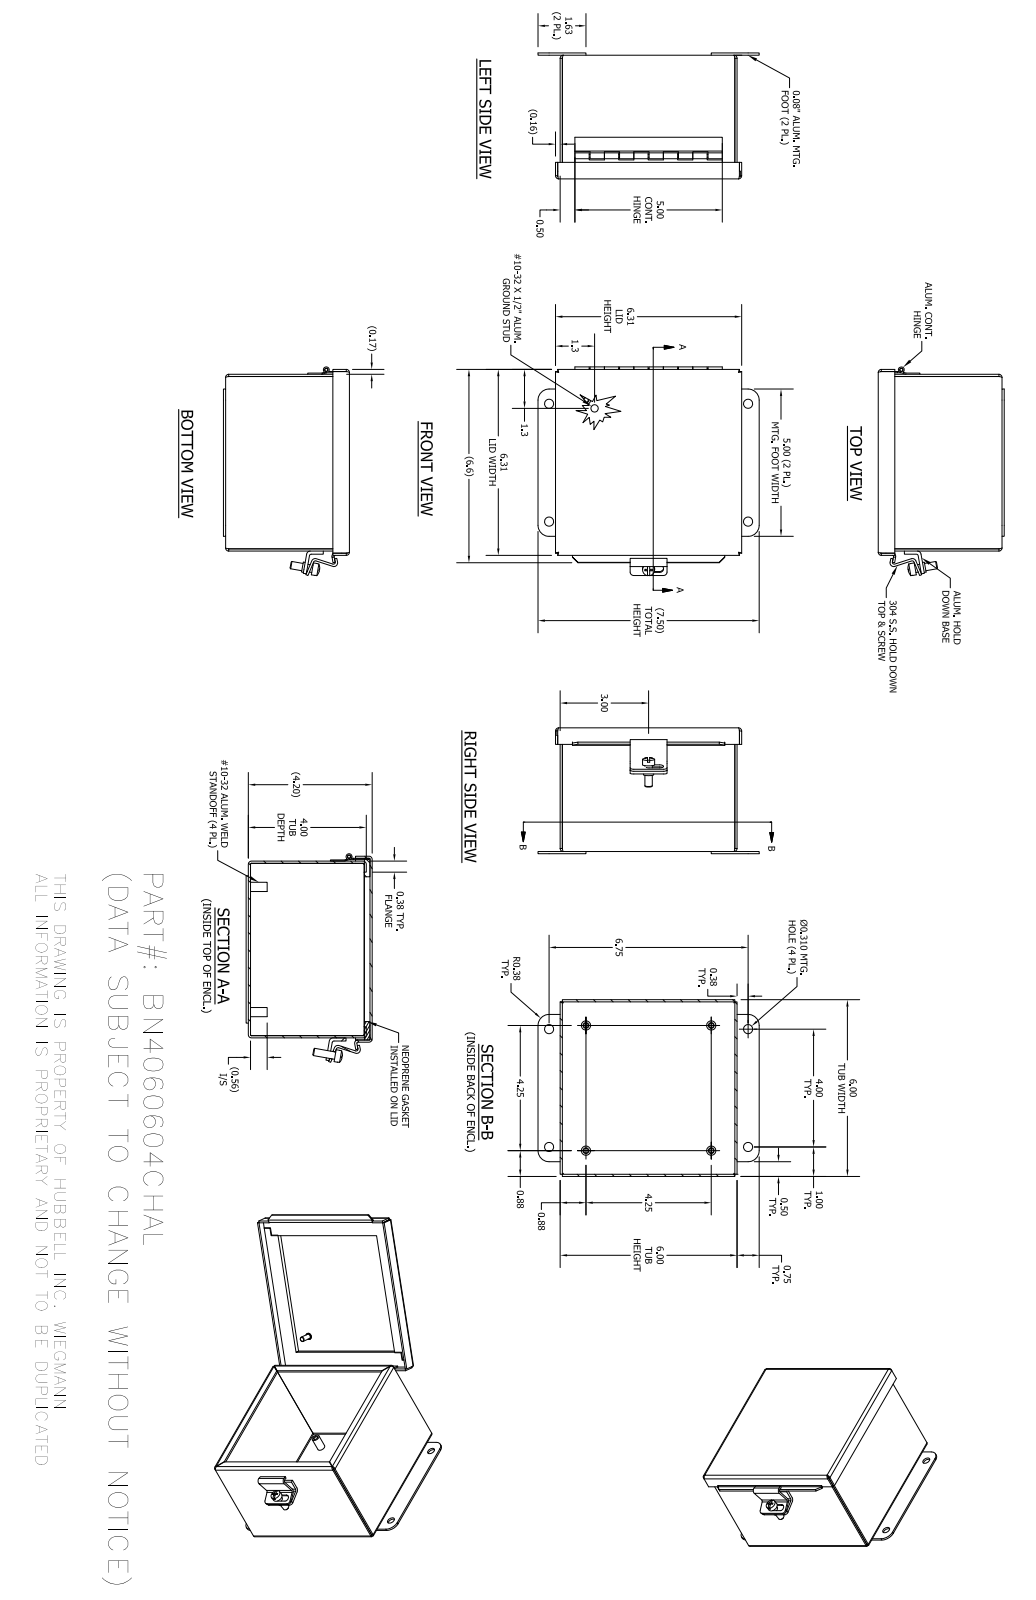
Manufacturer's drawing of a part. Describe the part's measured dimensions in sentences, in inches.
The part is named "B_060604_ALBKP; 32840TH; 32840LH; 32840P (+8 more)". Its 3-D file was written by "Autodesk Inventor 2016 (AUTOMOTIVE_DESIGN)". It is 17 solids with 330 faces: 203 planar, 89 cylindrical and 38 other. Overall it measures 7.5 by 7.086 by 4.274 inches. Its volume is 18.4 cubic inches and its surface area 479.9 square inches. Round holes: 4 of diameter 0.156, 4 of diameter 0.25, 4 of diameter 0.31, 1 of diameter 0.117, 1 of diameter 0.196. Round bosses or shafts: 6 of diameter 0.25, 4 of diameter 0.313, 1 of diameter 0.409, 1 of diameter 0.344, 1 of diameter 0.2, 1 of diameter 0.19, 1 of diameter 0.1. Partial cylindrical surfaces (rounded edges, fillets, slot ends): 13 of radius 0.031, 13 of radius 0.105, 4 of radius 0.125, 4 of radius 0.375, 3 of radius 0.063, 3 of radius 0.126, 2 of radius 0.133. The main face-to-face distances are 0.074, 5.926, 4.125, 6, 5.852, 4.199, 4.051, 4.2, 3.937, 3.863. The hole center spacings are 4.25, 4.31, 1.256, 5.502, 6.01, 6.875, 6.875, 1.256.
